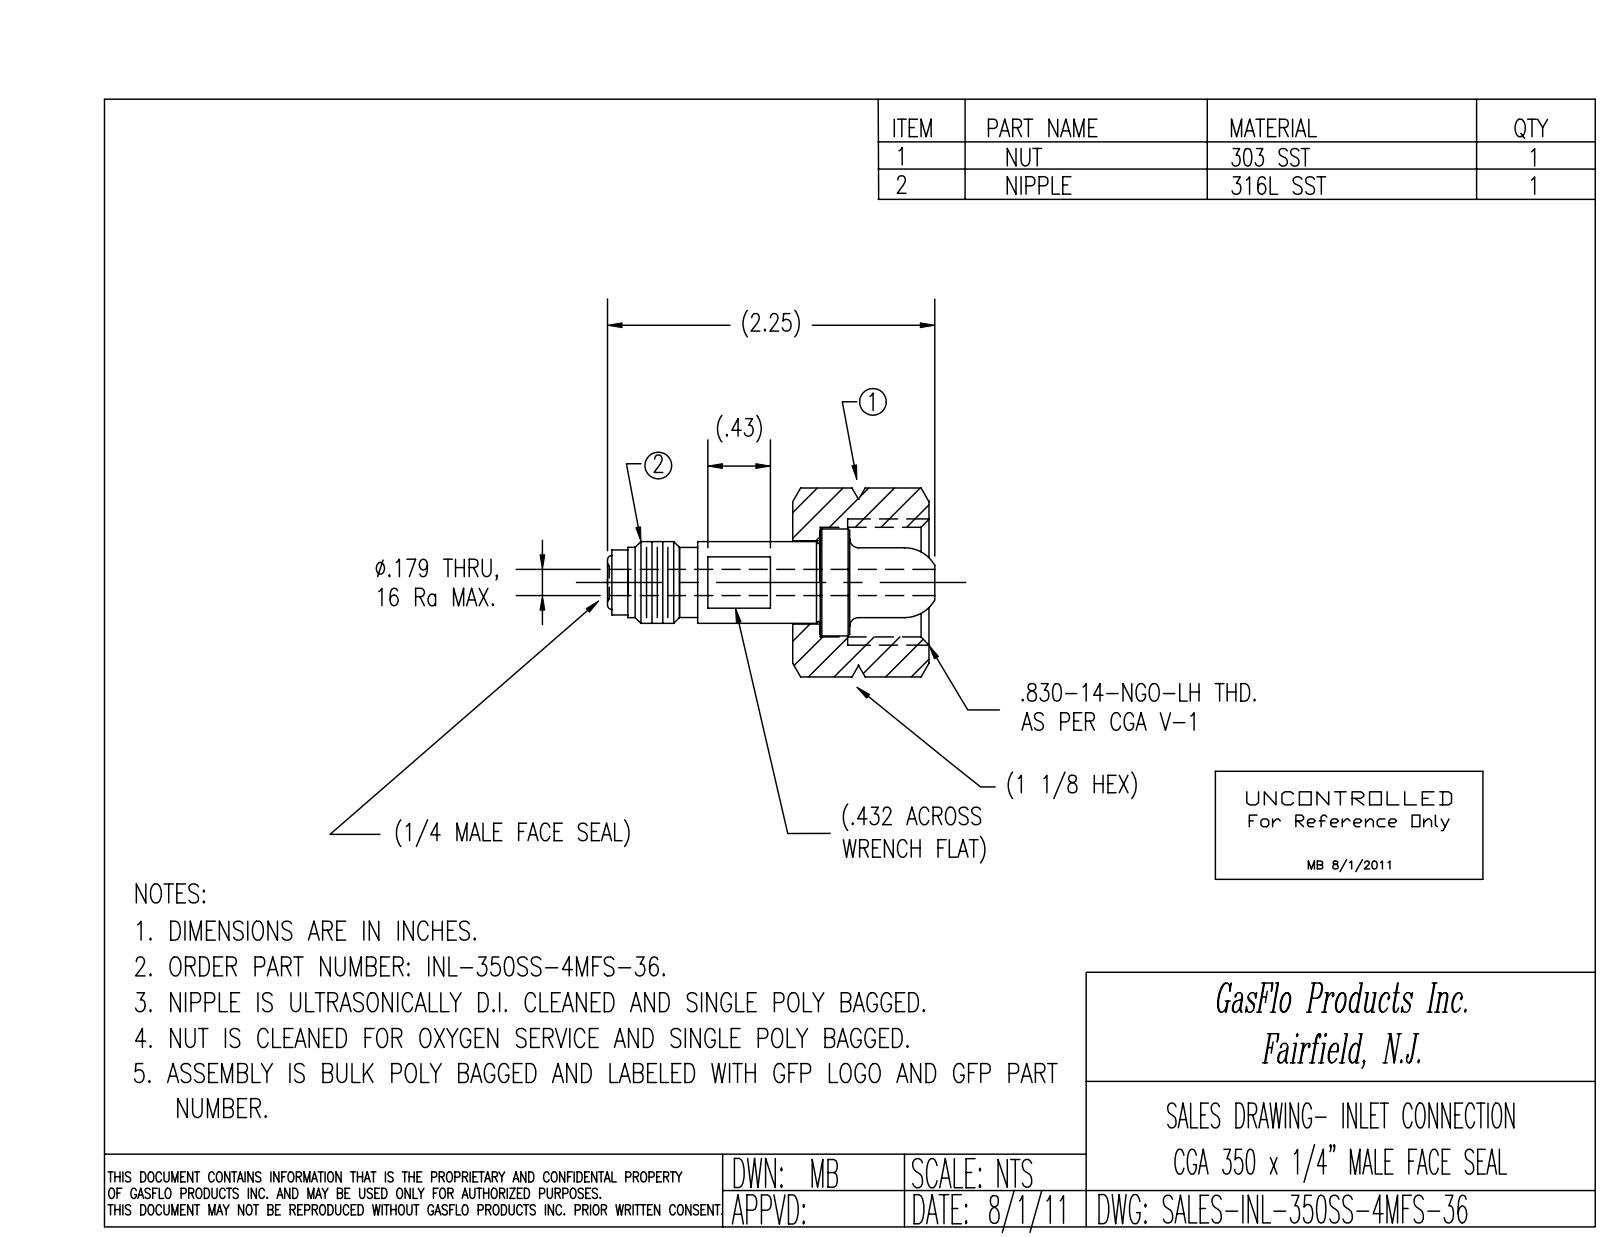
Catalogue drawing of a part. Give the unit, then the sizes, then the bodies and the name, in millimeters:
Units: millimetres
Overall size (bounding box): 57.2 × 33 × 28.6
Round holes (diameter × count): ⌀4.6 ×1, ⌀5.9 ×1, ⌀14.5 ×1, ⌀19.2 ×1
Round bosses / shafts (diameter × count): ⌀18.7 ×1, ⌀14.2 ×1, ⌀14.1 ×1, ⌀12.2 ×1, ⌀12.1 ×1, ⌀11.3 ×1, ⌀10 ×1
Main face-to-face distances: 28.6, 28.6, 24, 5, 19, 8.8, 19.8, 11, 9.9, 4.9
Volume: 17 340 mm³ · Surface area: 9 116 mm²
Bodies: 2 solids, 203 faces (41 planar, 42 cylindrical, 120 other)
Part name (STEP PRODUCT): INL-350SS-4MFS-36
STEP written by: SolidWorks 2018 (CONFIG_CONTROL_DESIGN)
